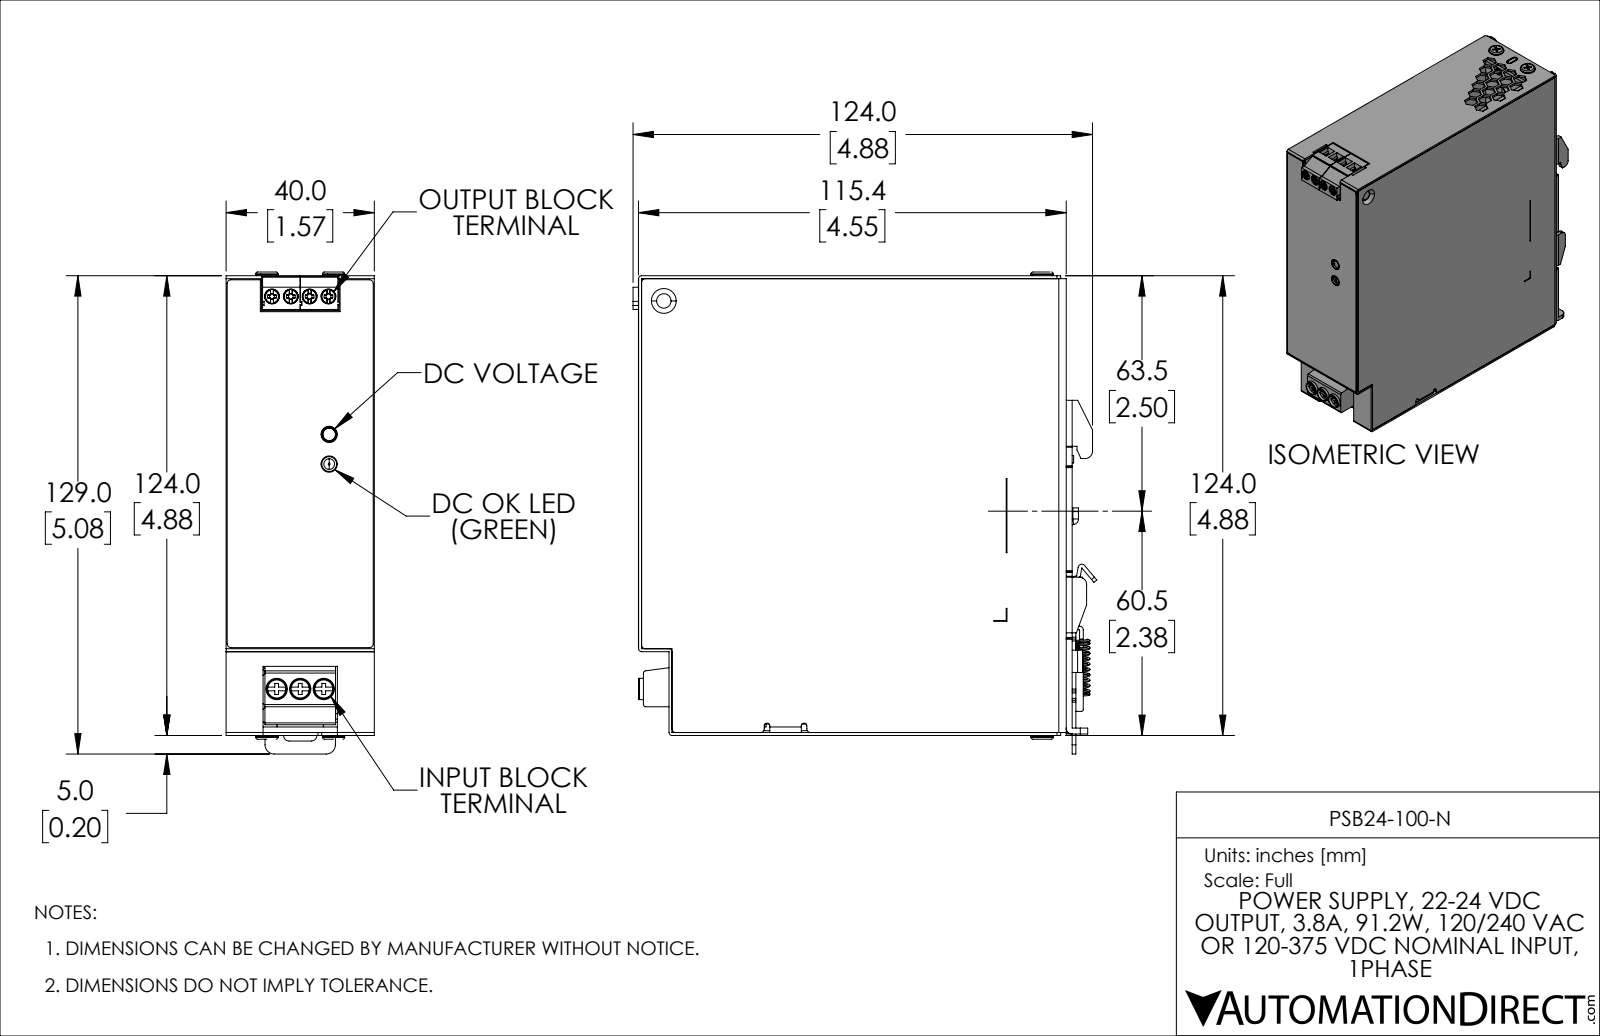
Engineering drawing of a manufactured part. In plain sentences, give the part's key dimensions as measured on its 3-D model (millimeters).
The part is named "PSB24-100-N". Its 3-D file was written by "SolidWorks 2019 (AUTOMOTIVE_DESIGN)". It is 31 solids with 2550 faces: 1958 planar, 466 cylindrical and 126 other. Overall it measures 130 by 125.1 by 40 millimeters. Its volume is 115 600 cubic millimeters and its surface area 211 200 square millimeters. Round holes: 8 of diameter 2.5, 7 of diameter 4, 4 of diameter 2, 4 of diameter 3.5, 3 of diameter 4.9, 2 of diameter 1, 2 of diameter 1.8, 2 of diameter 3.8, 2 of diameter 3.9, 2 of diameter 4.4, 1 of diameter 3, 1 of diameter 3.7. Round bosses or shafts: 4 of diameter 3.9, 3 of diameter 5.7, 3 of diameter 4.5, 2 of diameter 6, 2 of diameter 5.5, 2 of diameter 2.3, 2 of diameter 2, 1 of diameter 4.6. Partial cylindrical surfaces (rounded edges, fillets, slot ends): 68 of radius 1, 60 of radius 0.3, 43 of radius 0.5, 18 of radius 0.1, 16 of radius 0.3, 14 of radius 0.2, 11 of radius 0.8, 8 of radius 2. The main face-to-face distances are 1.5, 0.4, 38.5, 1.9, 37, 38.1, 36.6, 1.6, 0.8, 40. The hole center spacings are 5.1, 9, 20, 6.1, 6.4, 10.2, 11.8, 13.
